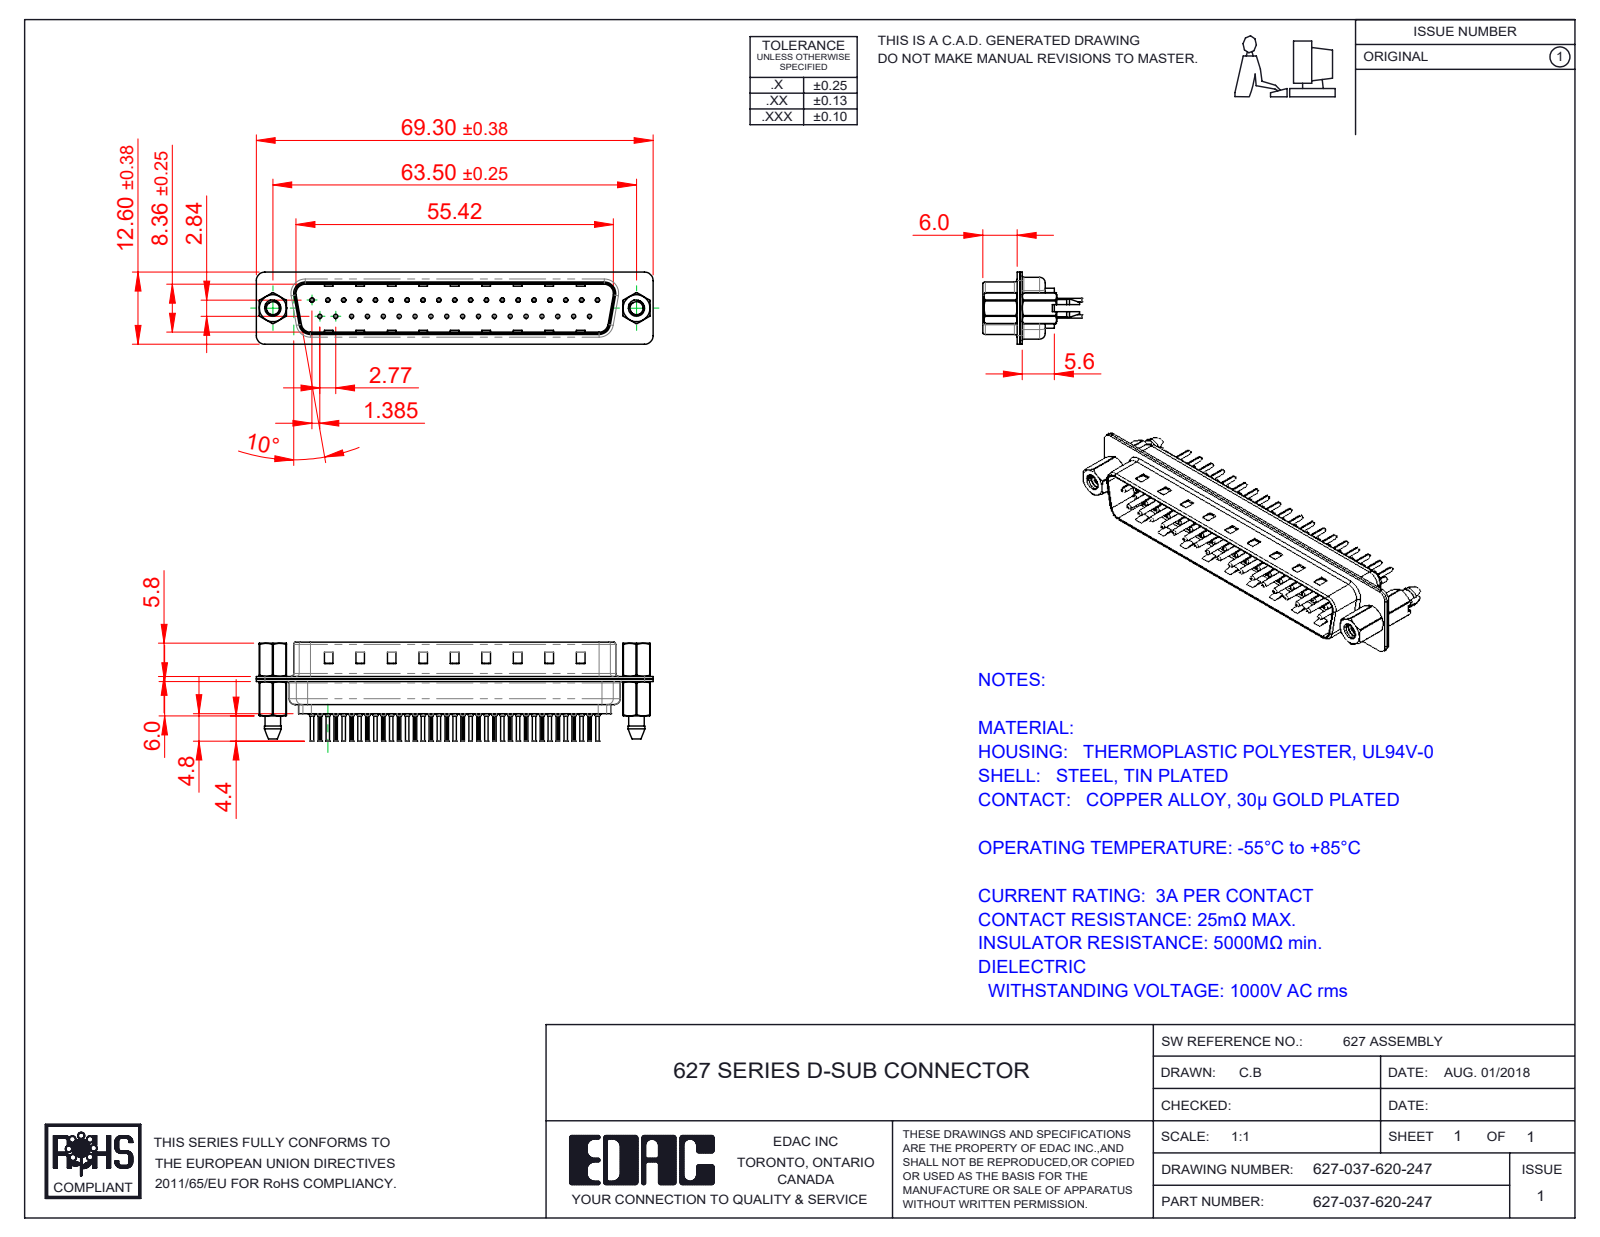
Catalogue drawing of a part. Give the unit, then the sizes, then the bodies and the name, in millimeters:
Units: millimetres
Overall size (bounding box): 69.3 × 17.3 × 12.6
Round holes (diameter × count): ⌀0.2 ×37, ⌀0.35 ×37, ⌀1.1 ×37, ⌀1.6 ×37, ⌀2.26 ×2, ⌀2.29 ×2, ⌀4 ×2, ⌀4.8 ×2
Round bosses / shafts (diameter × count): ⌀2 ×37, ⌀1.5 ×37, ⌀0.75 ×37, ⌀0.6 ×37, ⌀4.9 ×2, ⌀2.79 ×2
Partial cylindrical surfaces — rounded edges, fillets, slot ends (radius × count): R0.1 ×74, R1.5 ×18, R2 ×12, R1.6 ×10, R0.5 ×8, R0.25 ×4, R0.6 ×4, R0.65 ×4
Main face-to-face distances: 0.4, 0.82, 9.58, 0.45, 8.76, 1.5, 0.9, 1.4, 6.5, 6.05
Hole centre spacings: 3.16, 2.77, 5.54, 8.31, 5.04, 10.1, 11.08, 12.78
Volume: 4 028 mm³ · Surface area: 11 455 mm²
Bodies: 44 solids, 4238 faces (1145 planar, 1614 cylindrical, 1479 other)
Part name (STEP PRODUCT): 627 Contact Row 2_20L; 627 Shell Front_37 Contacts; 627 Contact Row 1_20L; 627 4-40 Hex Standoff (+4 more)
STEP written by: SolidWorks 2020 (CONFIG_CONTROL_DESIGN)
